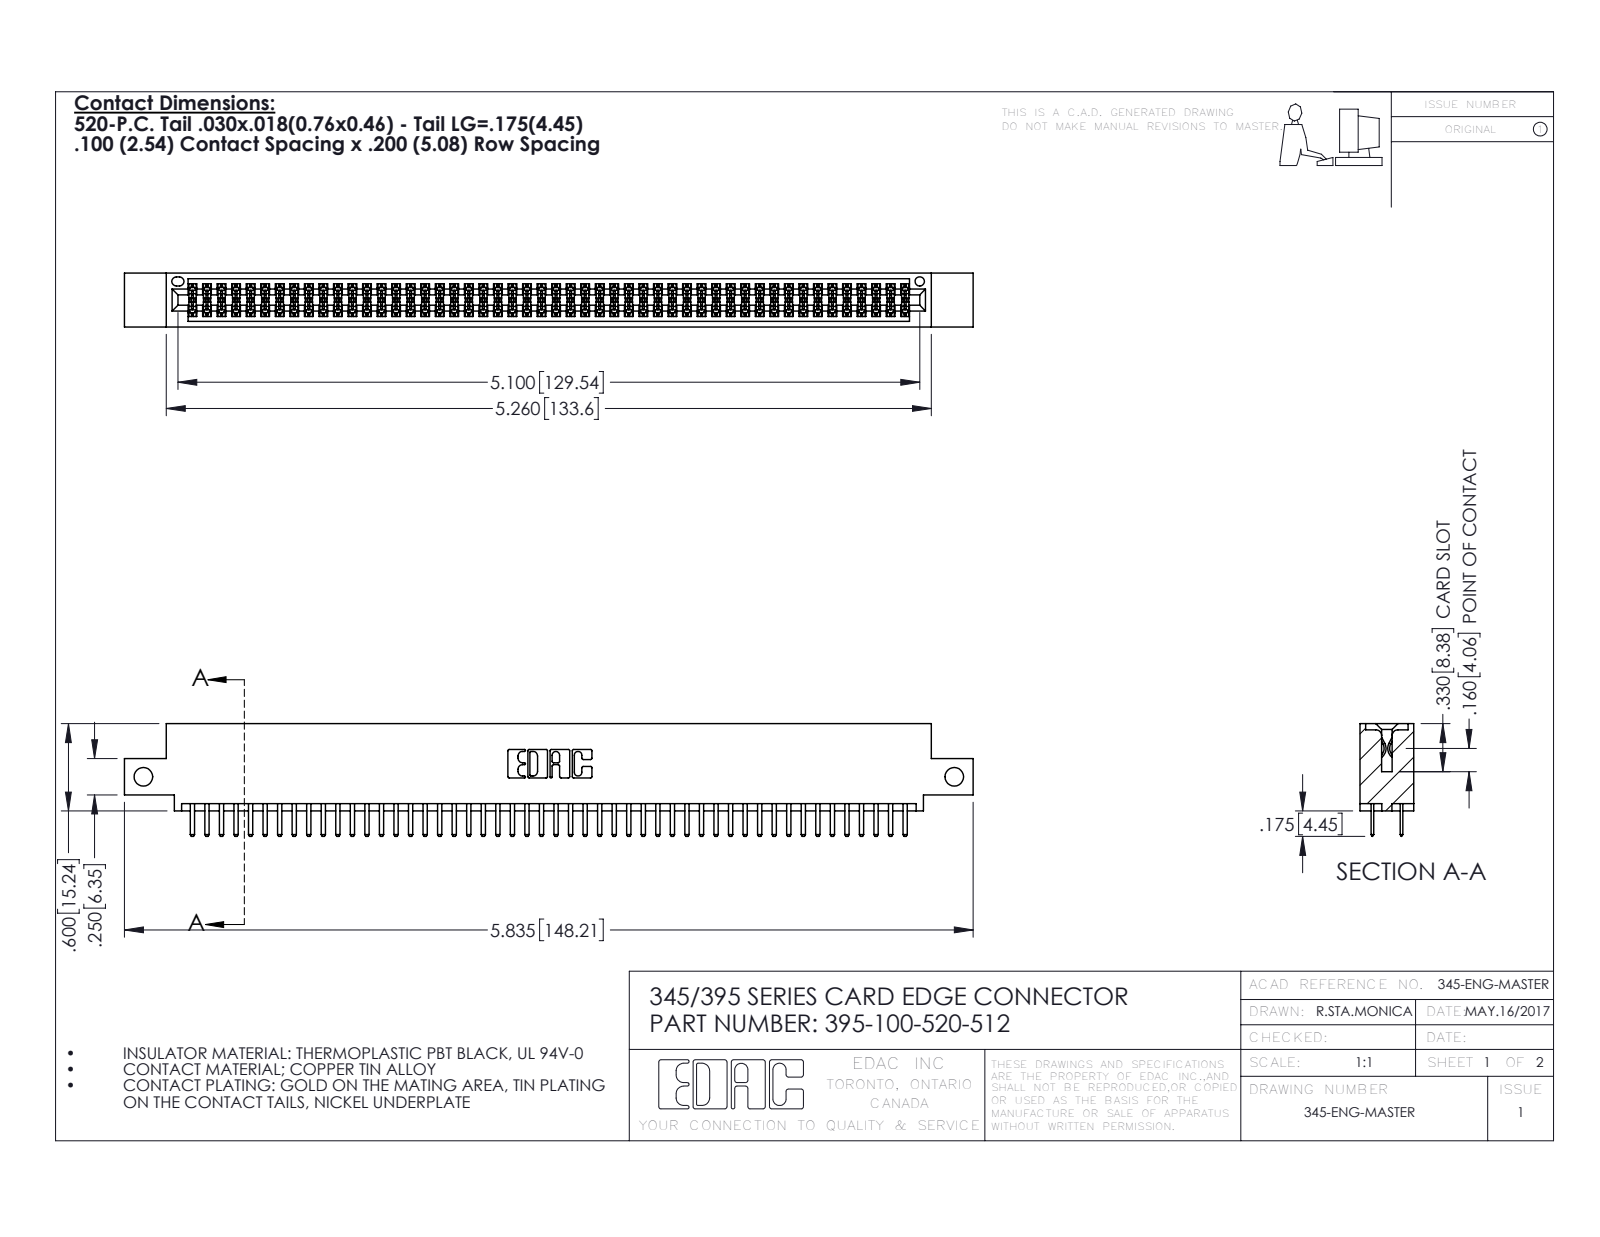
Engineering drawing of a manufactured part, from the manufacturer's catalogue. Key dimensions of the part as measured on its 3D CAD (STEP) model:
Part name (STEP PRODUCT): 395-100-520-512; 345-292-001_345-293-120; 345 Part_0.110 Offset - Side Mount
STEP written by: SolidWorks 2016 (CONFIG_CONTROL_DESIGN)
Units: inches
Bodies: 101 solids, 5530 faces (3584 planar, 1946 cylindrical, 0 other)
Overall size (bounding box): 5.835 × 0.775 × 0.37
Volume: 0.871 in³ · Surface area: 32.72 in²
Round holes (diameter × count): ⌀0.128 ×2, ⌀0.064 ×1
Partial cylindrical surfaces — rounded edges, fillets, slot ends (radius × count): R0.006 ×150, R0.01 ×104, R0.01 ×22, R0.007 ×6, R0.031 ×6, R0.026 ×3, R0.014 ×2, R0.019 ×2
Main face-to-face distances: 0.298, 0.072, 0.2, 0.37, 0.098, 0.272, 0.025, 0.225, 0.022, 0.072
Hole centre spacings: 5.575
